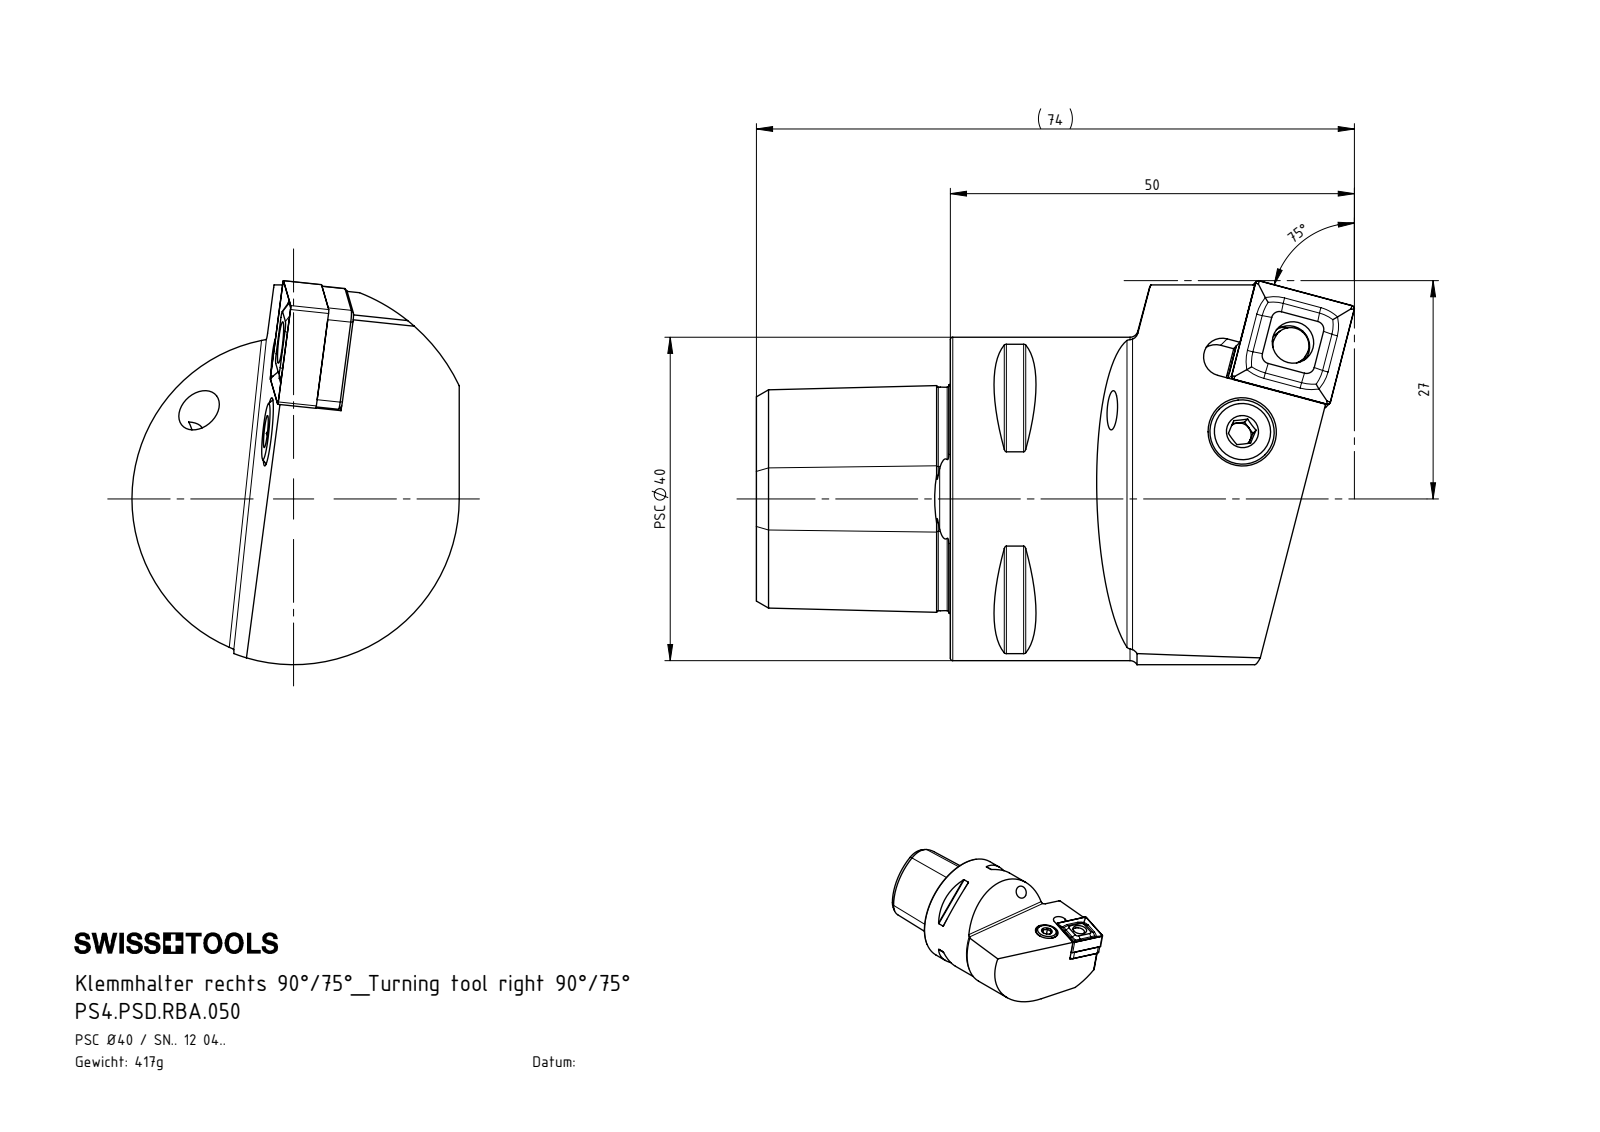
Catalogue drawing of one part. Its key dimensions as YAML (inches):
part_name: "KVT_MB_600_050; WCD-ER1.101.000; PS4-PSD.RBA.050_A_Fertigbearbeitung; WCD-ER4.101.017_A (+4 more)"
step_written_by: "SolidWorks 2017 (AUTOMOTIVE_DESIGN)"
units: inches
bodies: {solids: 8, faces: 261, planar: 89, cylindrical: 55, other: 117}
overall_size: [2.913, 1.87, 1.594]
volume: 3.211
surface_area: 23.92
round_holes:
  - {diameter: 0.157, count: 2}
  - {diameter: 0.165, count: 2}
  - {diameter: 0.181, count: 1}
  - {diameter: 0.203, count: 1}
  - {diameter: 0.252, count: 1}
  - {diameter: 0.276, count: 1}
  - {diameter: 0.331, count: 1}
  - {diameter: 0.492, count: 1}
  - {diameter: 0.709, count: 1}
  - {diameter: 0.787, count: 1}
round_bosses_or_shafts:
  - {diameter: 1.575, count: 1}
  - {diameter: 0.315, count: 1}
  - {diameter: 0.311, count: 1}
  - {diameter: 0.252, count: 1}
  - {diameter: 0.197, count: 1}
  - {diameter: 0.177, count: 1}
  - {diameter: 0.14, count: 1}
partial_cylinders:
  - {radius: 0.012, count: 8}
  - {radius: 0.016, count: 4}
  - {radius: 0.047, count: 4}
  - {radius: 0.098, count: 2}
  - {radius: 0.126, count: 2}
  - {radius: 0.031, count: 1}
  - {radius: 0.087, count: 1}
  - {radius: 0.093, count: 1}
face_to_face_distances: [0.125, 0.48, 0.5, 0.945, 0.176, 0.611, 0.176, 0.126, 0.301, 0.185]
hole_center_spacings: [0.504, 0.925]
